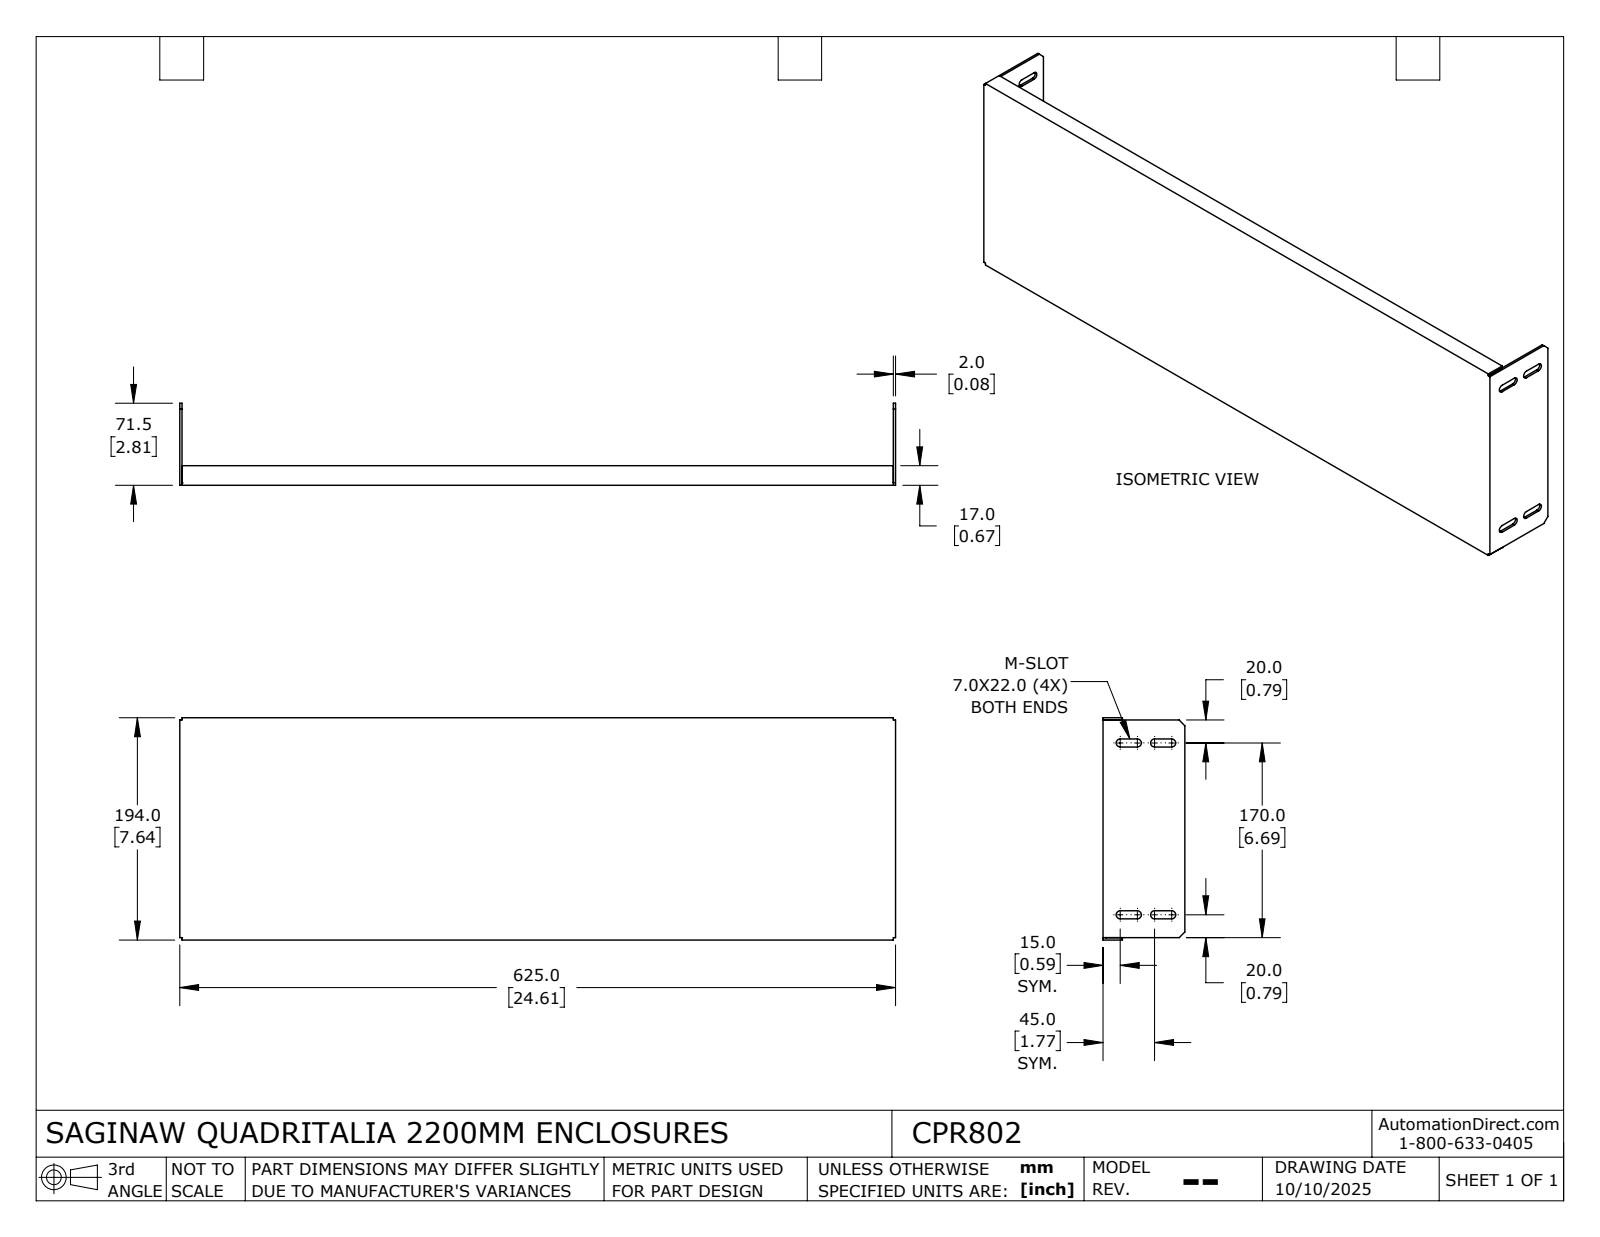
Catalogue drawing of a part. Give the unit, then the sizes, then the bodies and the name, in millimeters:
Units: millimetres
Overall size (bounding box): 625 × 194 × 71.5
Partial cylindrical surfaces — rounded edges, fillets, slot ends (radius × count): R3.5 ×8
Main face-to-face distances: 2, 623, 192, 625, 621, 194, 190, 17, 15, 71.5
Volume: 330 151 mm³ · Surface area: 334 911 mm²
Bodies: 1 solid, 59 faces (43 planar, 16 cylindrical, 0 other)
Part name (STEP PRODUCT): CPR802_Default
STEP written by: SolidWorks 2024 (CONFIG_CONTROL_DESIGN)
